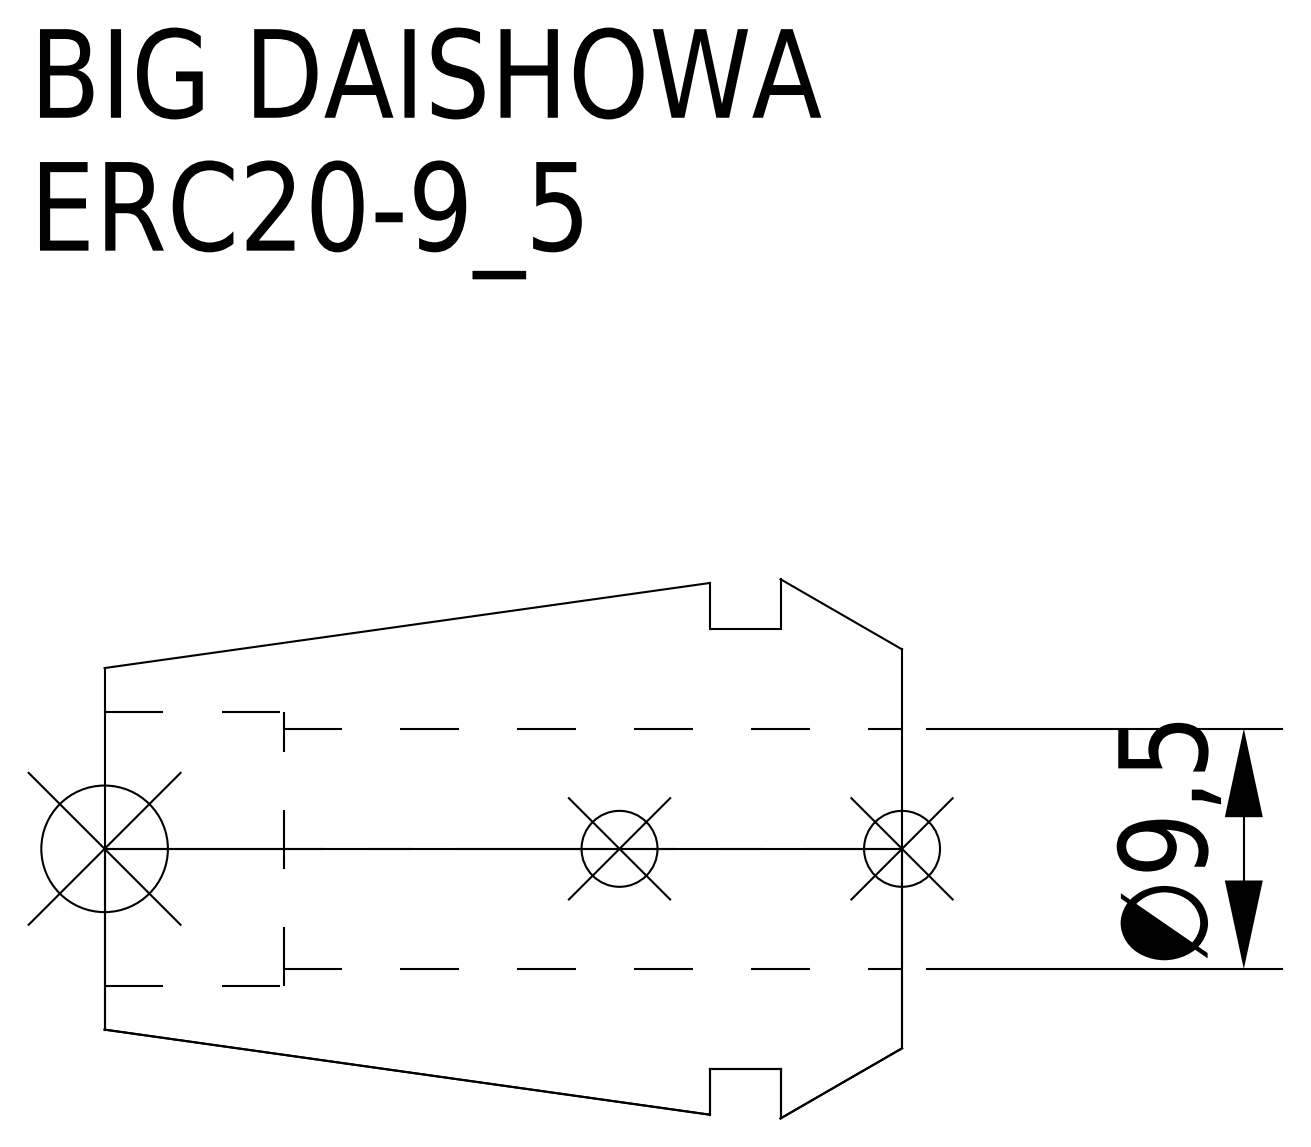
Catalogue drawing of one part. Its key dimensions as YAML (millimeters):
part_name: "ERC20-9_5"
step_written_by: "CREO PARAMETRIC BY PTC INC, 2016380 (AUTOMOTIVE_DESIGN)"
units: millimeters
bodies: {solids: 1, faces: 15, planar: 5, cylindrical: 6, other: 4}
overall_size: [31.5, 21.3, 21.3]
volume: 5503
surface_area: 3223
round_holes:
  - {diameter: 9.5, count: 1}
  - {diameter: 10.8, count: 1}
round_bosses_or_shafts:
  - {diameter: 17.4, count: 1}
face_to_face_distances: [4.8, 7.6, 2.8, 31.5, 26.7, 23.9, 24.43, 19.63, 16.83, 7.07]
